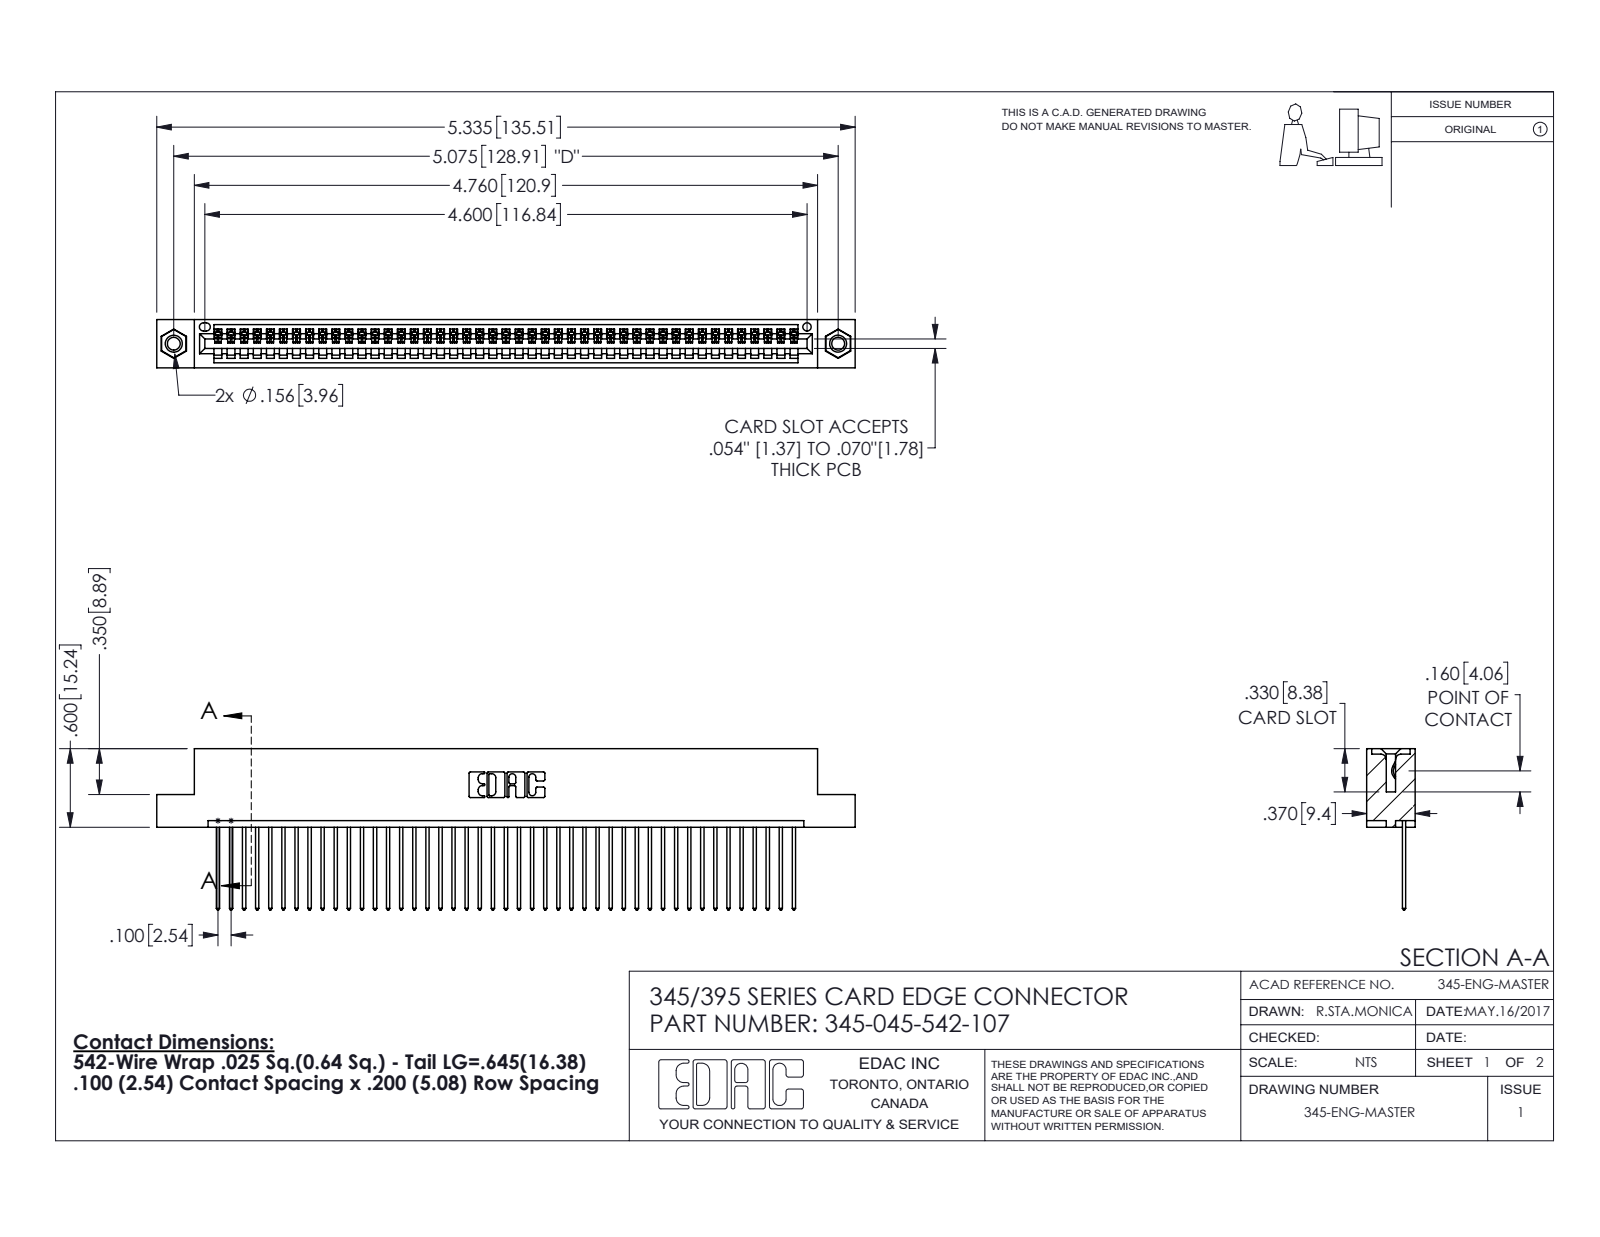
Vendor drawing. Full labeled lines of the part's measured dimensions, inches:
Part name (STEP PRODUCT): 345-045-542-107; 345 Part_Flush Mounting Lugs - 0.156 Dia-TI; 345-250-001_345-250-005-103; 345-292-001_345-293-142
STEP written by: SolidWorks 2016 (CONFIG_CONTROL_DESIGN)
Units: inches
Bodies: 48 solids, 2796 faces (1912 planar, 868 cylindrical, 16 other)
Overall size (bounding box): 5.335 × 1.232 × 0.37
Volume: 0.792 in³ · Surface area: 27.84 in²
Round holes (diameter × count): ⌀0.098 ×2, ⌀0.125 ×2, ⌀0.156 ×2, ⌀0.064 ×1
Round bosses / shafts (diameter × count): ⌀0.155 ×2
Partial cylindrical surfaces — rounded edges, fillets, slot ends (radius × count): R0.006 ×90, R0.01 ×90, R0.01 ×22, R0.007 ×6, R0.031 ×6, R0.026 ×3, R0.031 ×2, R0.04 ×2
Main face-to-face distances: 0.072, 0.298, 0.37, 0.098, 0.272, 0.025, 0.2, 0.225, 0.149, 0.072
Hole centre spacings: 0.27, 4.839, 5.075
